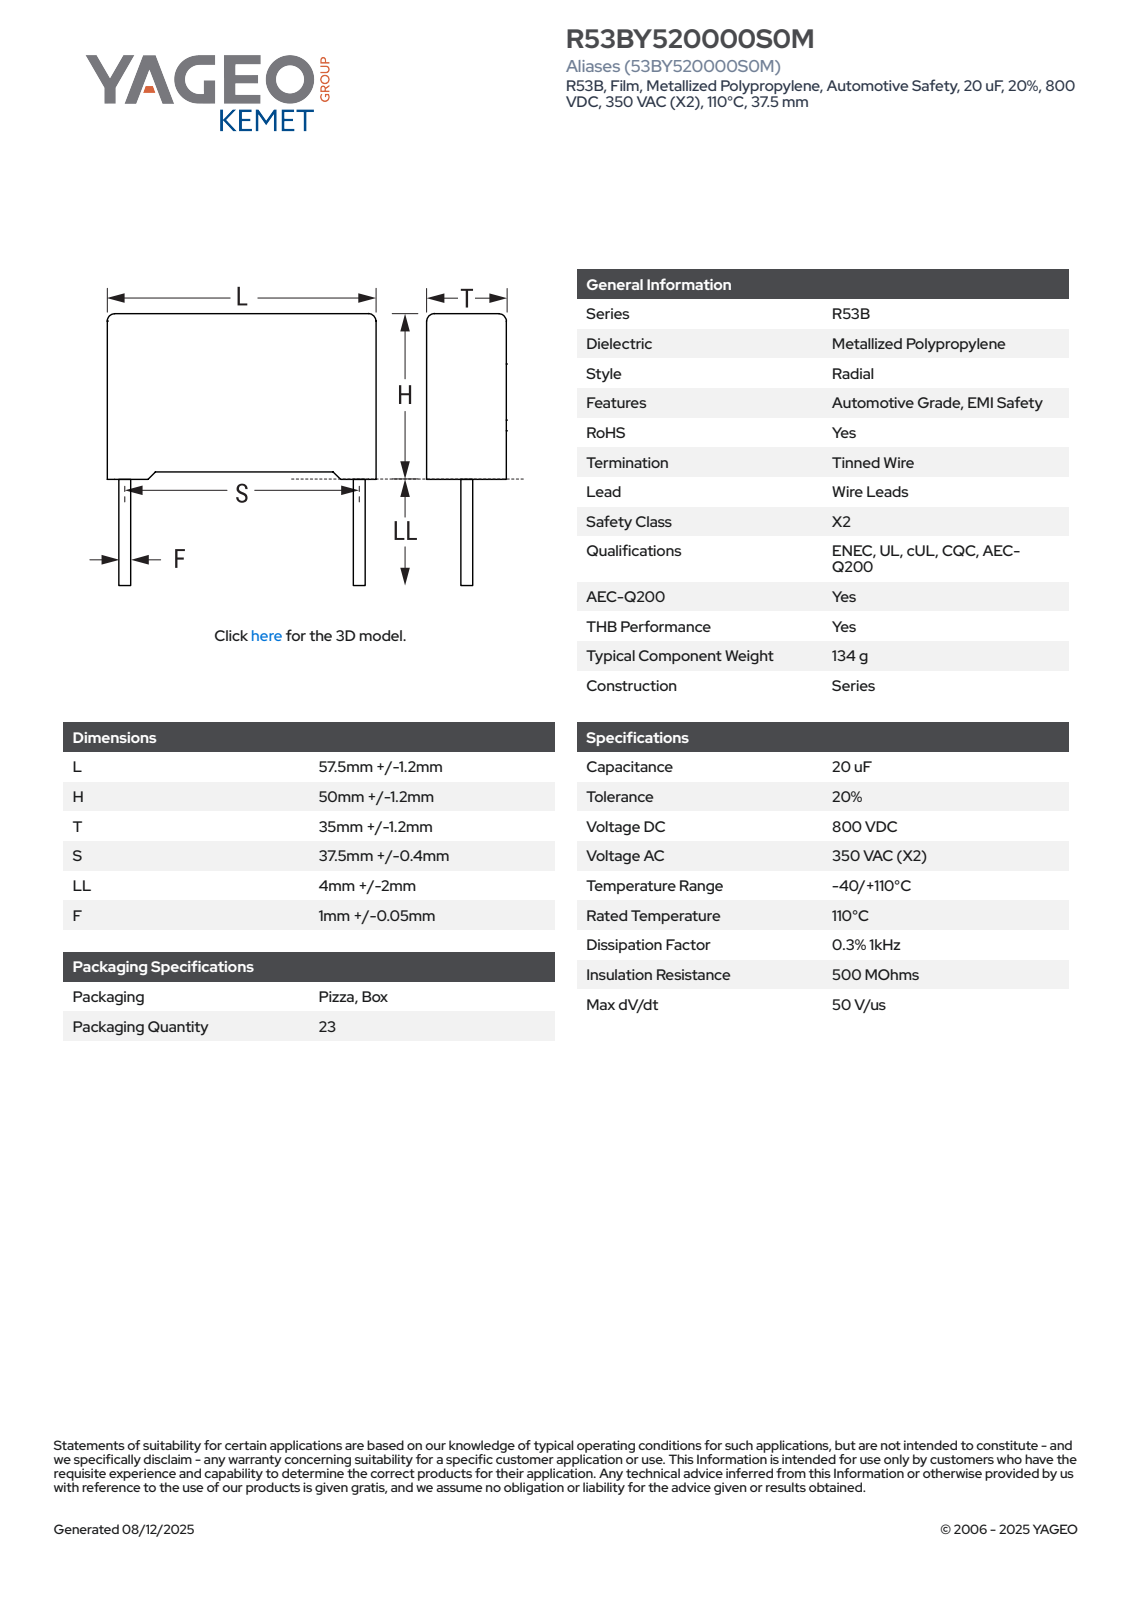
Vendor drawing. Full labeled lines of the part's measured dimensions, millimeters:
Part name (STEP PRODUCT): CFR_RB2_57.5X50X35_L58.7H51.2T36.2S37.5LL6F1.05
STEP written by: SolidWorks 2021 (AUTOMOTIVE_DESIGN)
Units: millimetres
Bodies: 4 solids, 85 faces (77 planar, 8 cylindrical, 0 other)
Overall size (bounding box): 58.7 × 57.2 × 36.2
Volume: 106 191 mm³ · Surface area: 14 227 mm²
Round bosses / shafts (diameter × count): ⌀1.05 ×2
Partial cylindrical surfaces — rounded edges, fillets, slot ends (radius × count): R0.5 ×4
Main face-to-face distances: 36.2, 58.7, 49.43, 1.02, 50.45, 0.75, 1.77, 51.2, 1.96, 56.74
